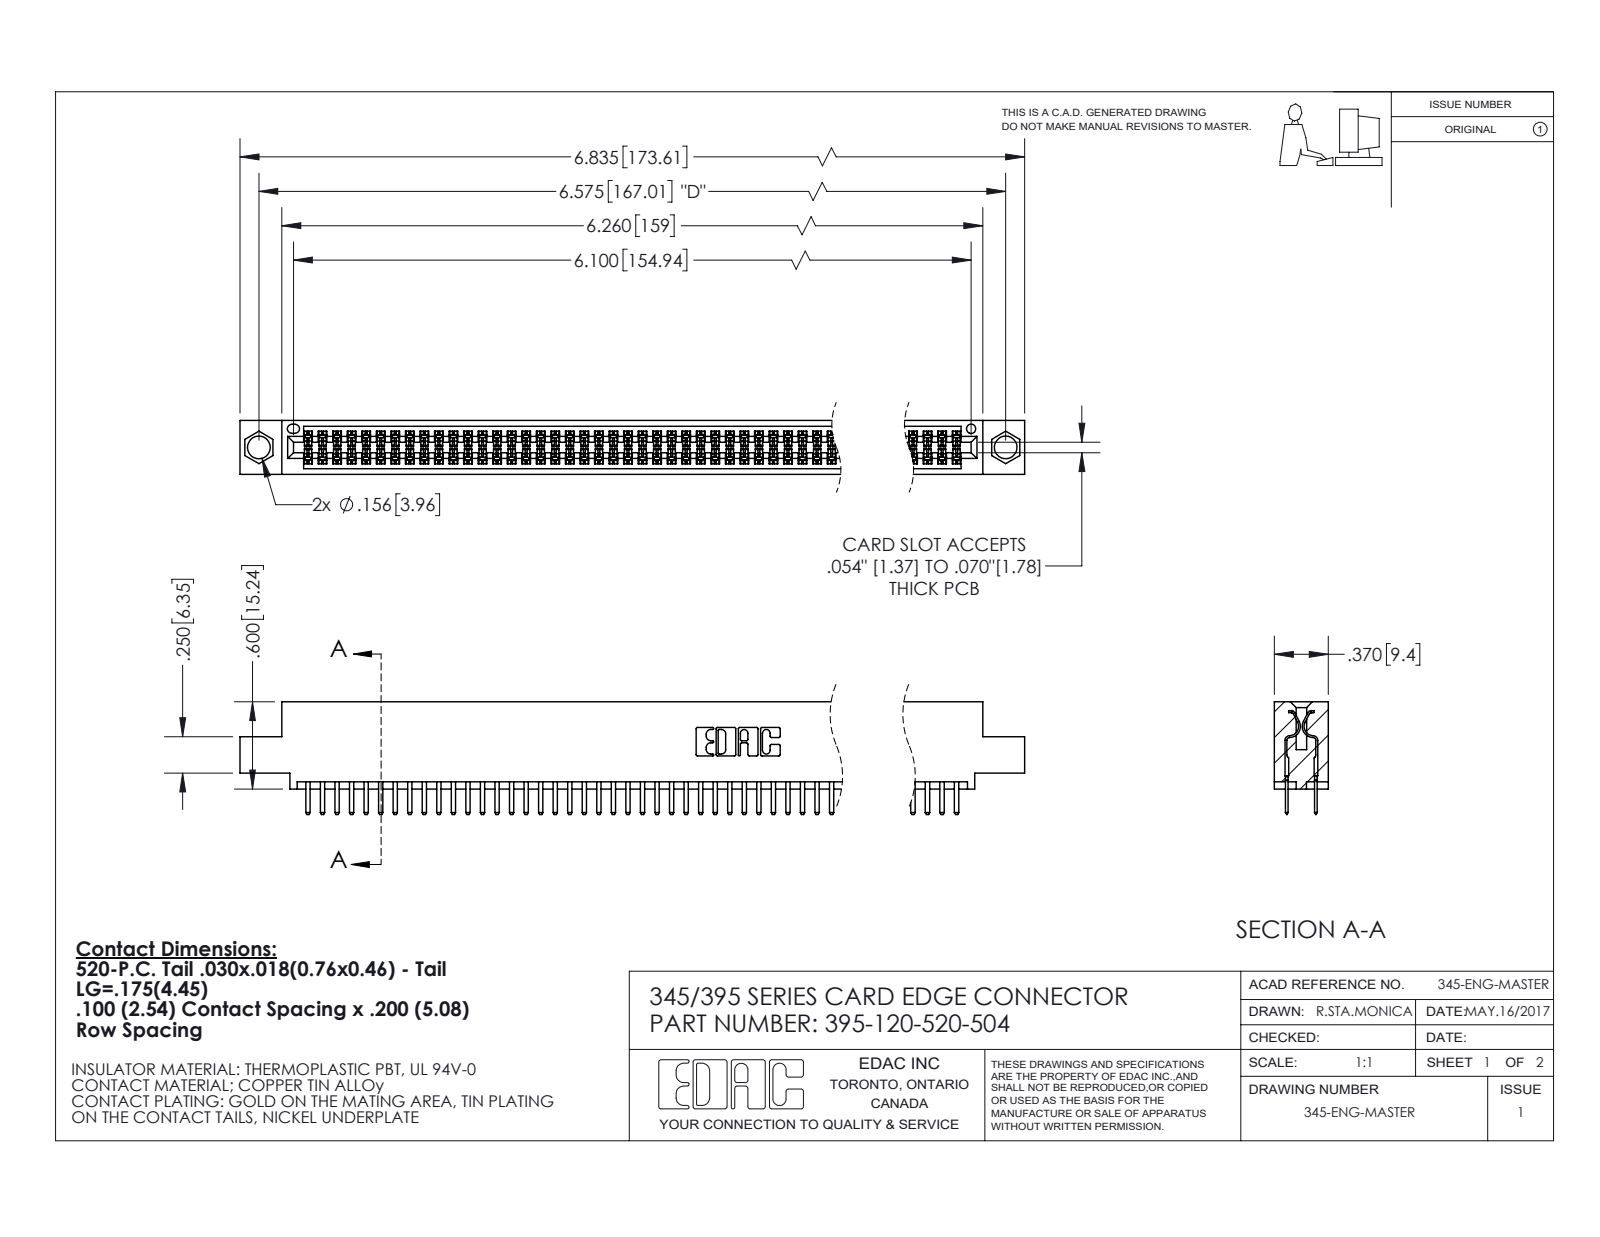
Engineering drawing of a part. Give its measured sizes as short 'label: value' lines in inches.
name: 345-292-001_345-293-120; 345 Part_0.110 Offset - 0.156 Dia-TI; 395-120-520-504
written by: SolidWorks 2020 (CONFIG_CONTROL_DESIGN)
unit: in
bodies: 121 solids, 6624 faces (4298 planar, 2326 cylindrical, 0 other)
size: 6.835 × 0.775 × 0.37
volume: 1.025 in³; area: 38.77 in²
holes: 2× ⌀0.156, 1× ⌀0.064
rounds: 180× R0.006, 124× R0.01, 22× R0.01, 6× R0.007, 6× R0.031, 3× R0.026, 2× R0.014, 2× R0.019
face distances: 0.298, 0.072, 0.2, 0.37, 0.098, 0.272, 0.025, 0.225, 0.022, 0.072
hole spacings: 0.27, 6.339, 6.575
